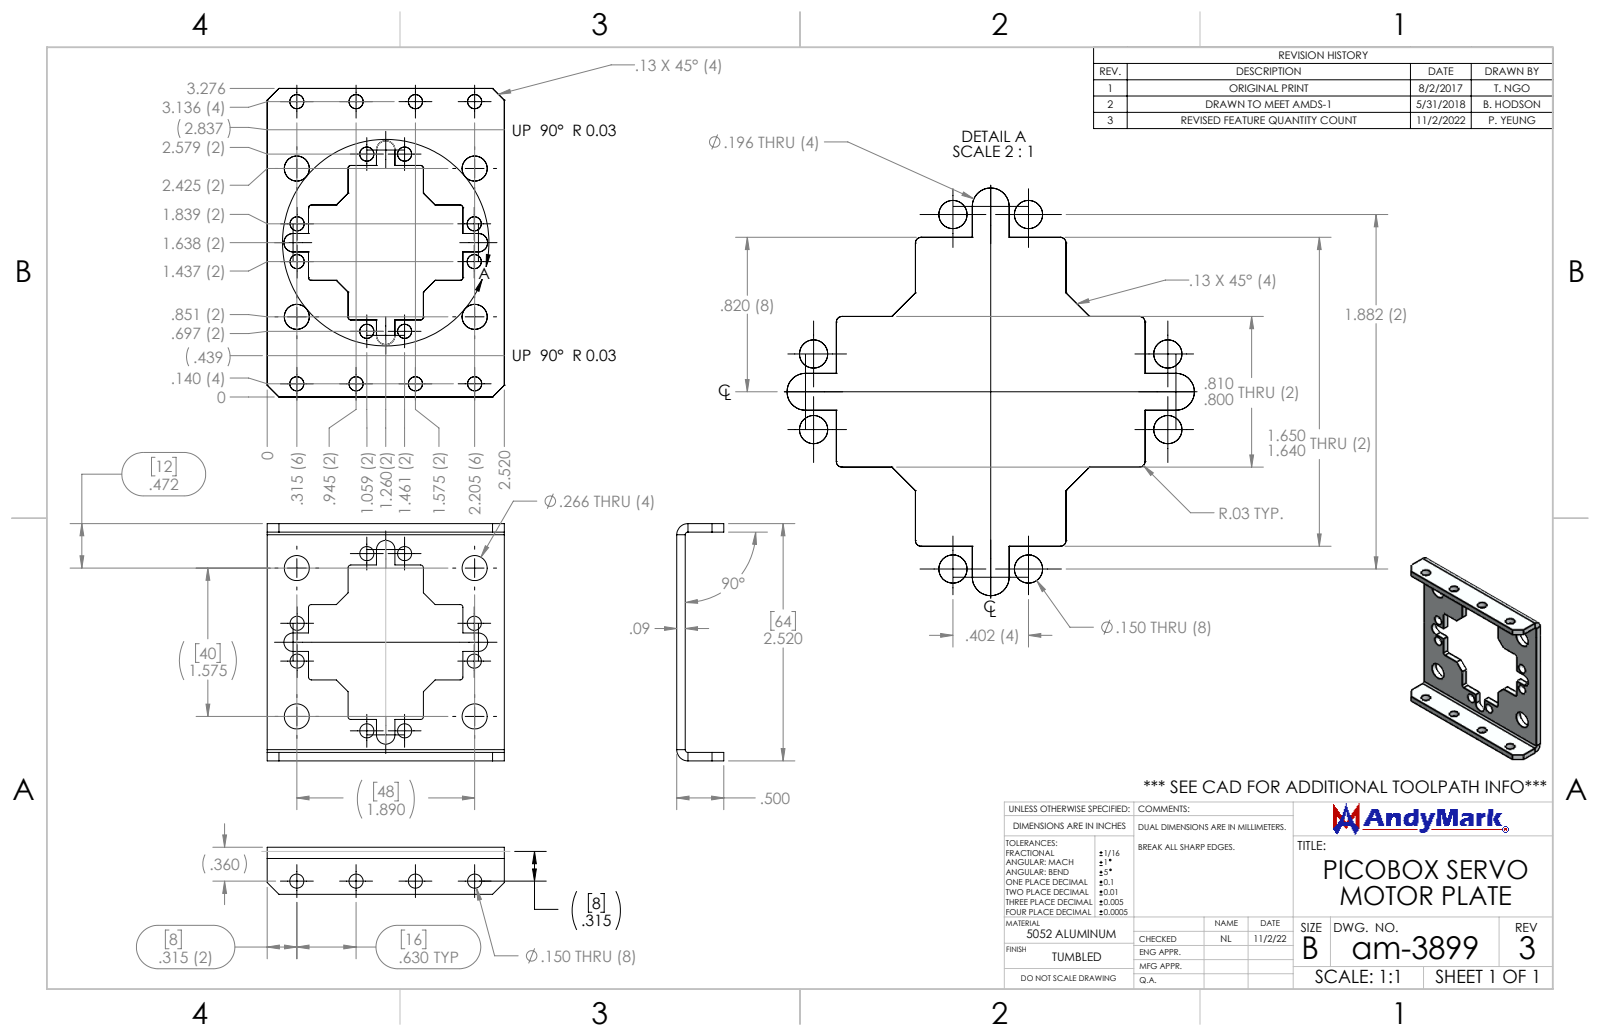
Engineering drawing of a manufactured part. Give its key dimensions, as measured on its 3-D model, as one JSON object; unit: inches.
{"part_name": "am-3899 PicoBox Servo Motor Plate", "step_written_by": "SolidWorks 2022 (CONFIG_CONTROL_DESIGN)", "units": "inches", "bodies": {"solids": 1, "faces": 107, "planar": 50, "cylindrical": 57, "other": 0}, "overall_size": [2.52, 2.52, 0.5], "volume_in3": 0.496, "surface_area_in2": 13.74, "round_holes": [[0.15, 12], [0.266, 4]], "partial_cylinders_radius": [[0.03, 8], [0.098, 4], [0.029, 2], [0.119, 2]], "face_to_face_distances": [0.09, 2.43, 2.52, 2.339, 0.5, 0.41, 0.44, 2.08, 0.86, 1.66], "hole_center_spacings": [1.361, 1.882, 0.402, 0.587, 0.76, 0.988, 1.047, 1.156]}
